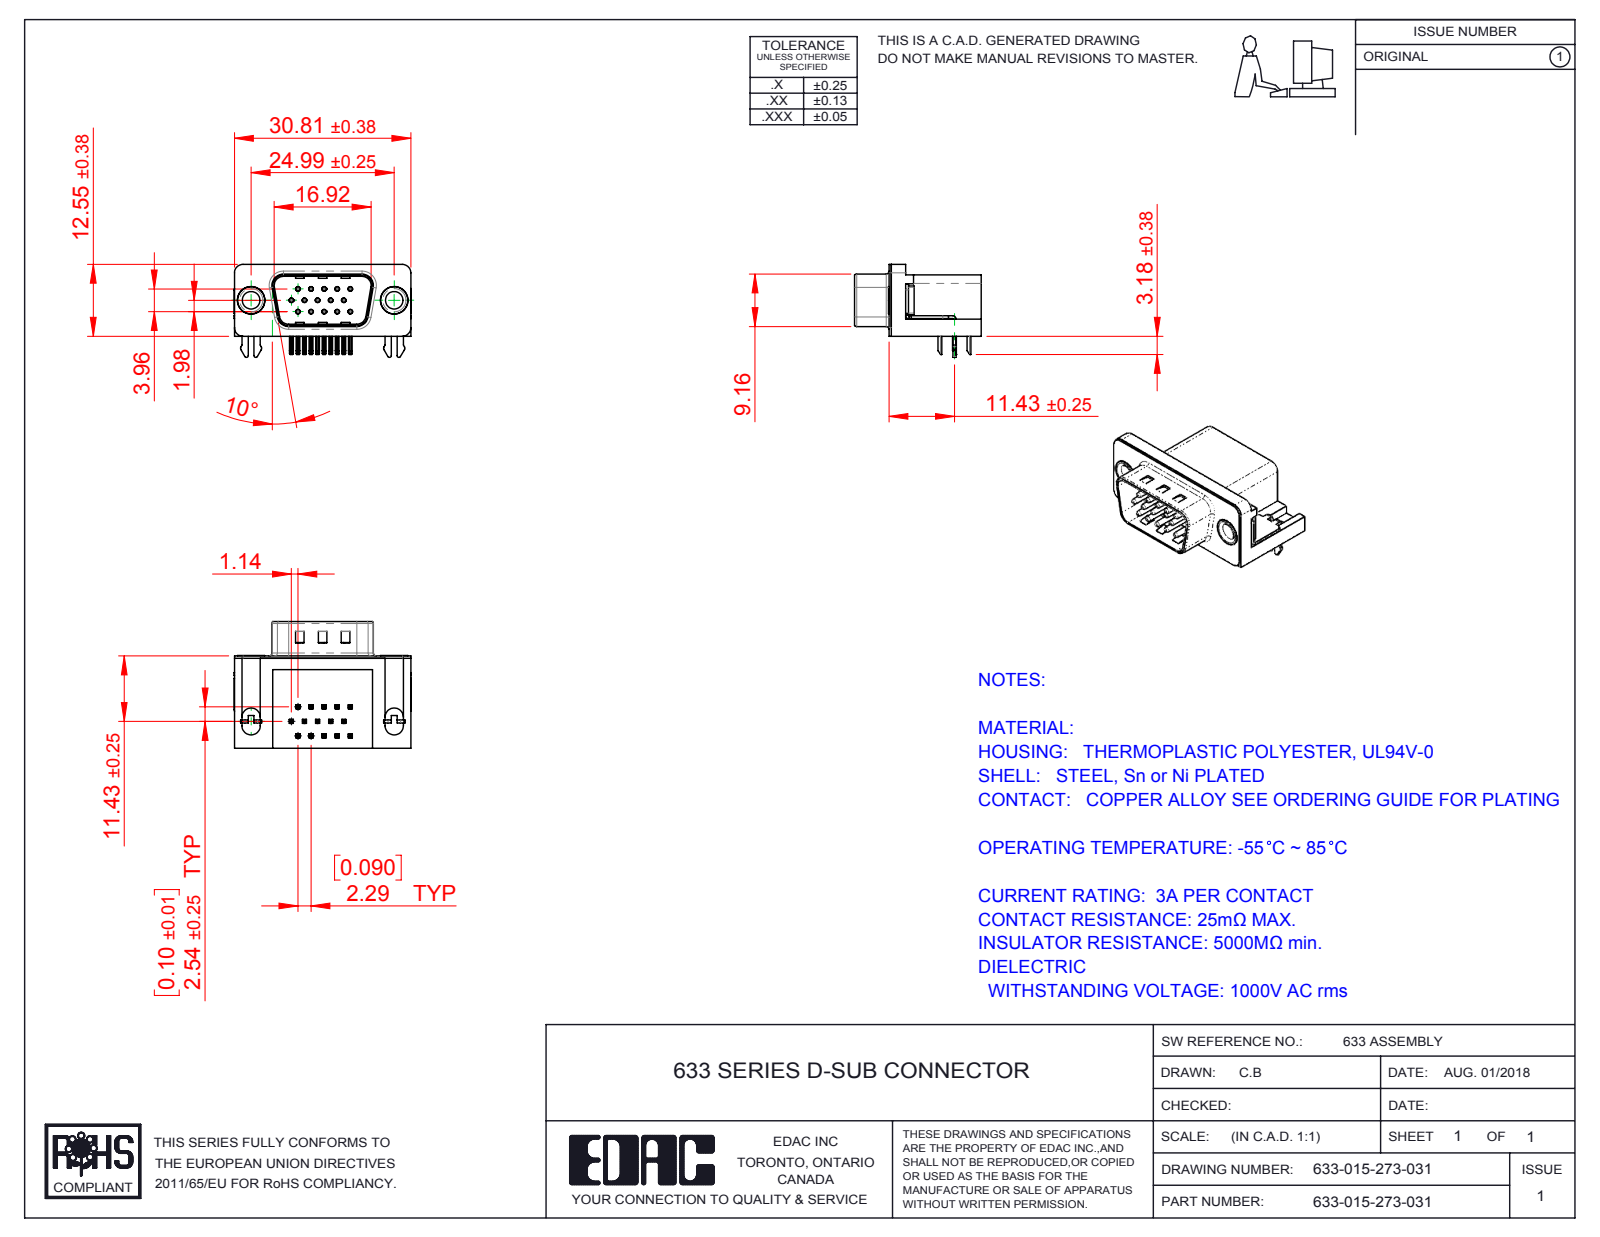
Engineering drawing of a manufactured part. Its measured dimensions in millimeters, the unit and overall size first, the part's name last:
Units: millimetres
Overall size (bounding box): 30.89 × 22.1 × 16.25
Round holes (diameter × count): ⌀0.35 ×15, ⌀0.8 ×15, ⌀3.05 ×2, ⌀4 ×2, ⌀4.8 ×2, ⌀5 ×2
Round bosses / shafts (diameter × count): ⌀0.75 ×15, ⌀4.9 ×2, ⌀4.75 ×2, ⌀3.85 ×2
Partial cylindrical surfaces — rounded edges, fillets, slot ends (radius × count): R0.25 ×68, R0.12 ×30, R1 ×16, R0.5 ×14, R1.6 ×8, R1.5 ×7, R0.32 ×4, R0.9 ×4
Main face-to-face distances: 0.4, 10.35, 15.7, 0.5, 2.9, 2.5, 6.7, 16.1, 0.35, 10.7
Hole centre spacings: 3.96, 2.28, 4.57, 2.29, 6.05, 6.86, 7.92, 6.04
Volume: 4 061 mm³ · Surface area: 5 407 mm²
Bodies: 21 solids, 1443 faces (893 planar, 433 cylindrical, 117 other)
Part name (STEP PRODUCT): 633 Contact Top; 633 Housing_15 Contact; 633 Shell_15 Contact; 633 2 Prong Board Lock (+5 more)
STEP written by: SolidWorks 2016 (CONFIG_CONTROL_DESIGN)
